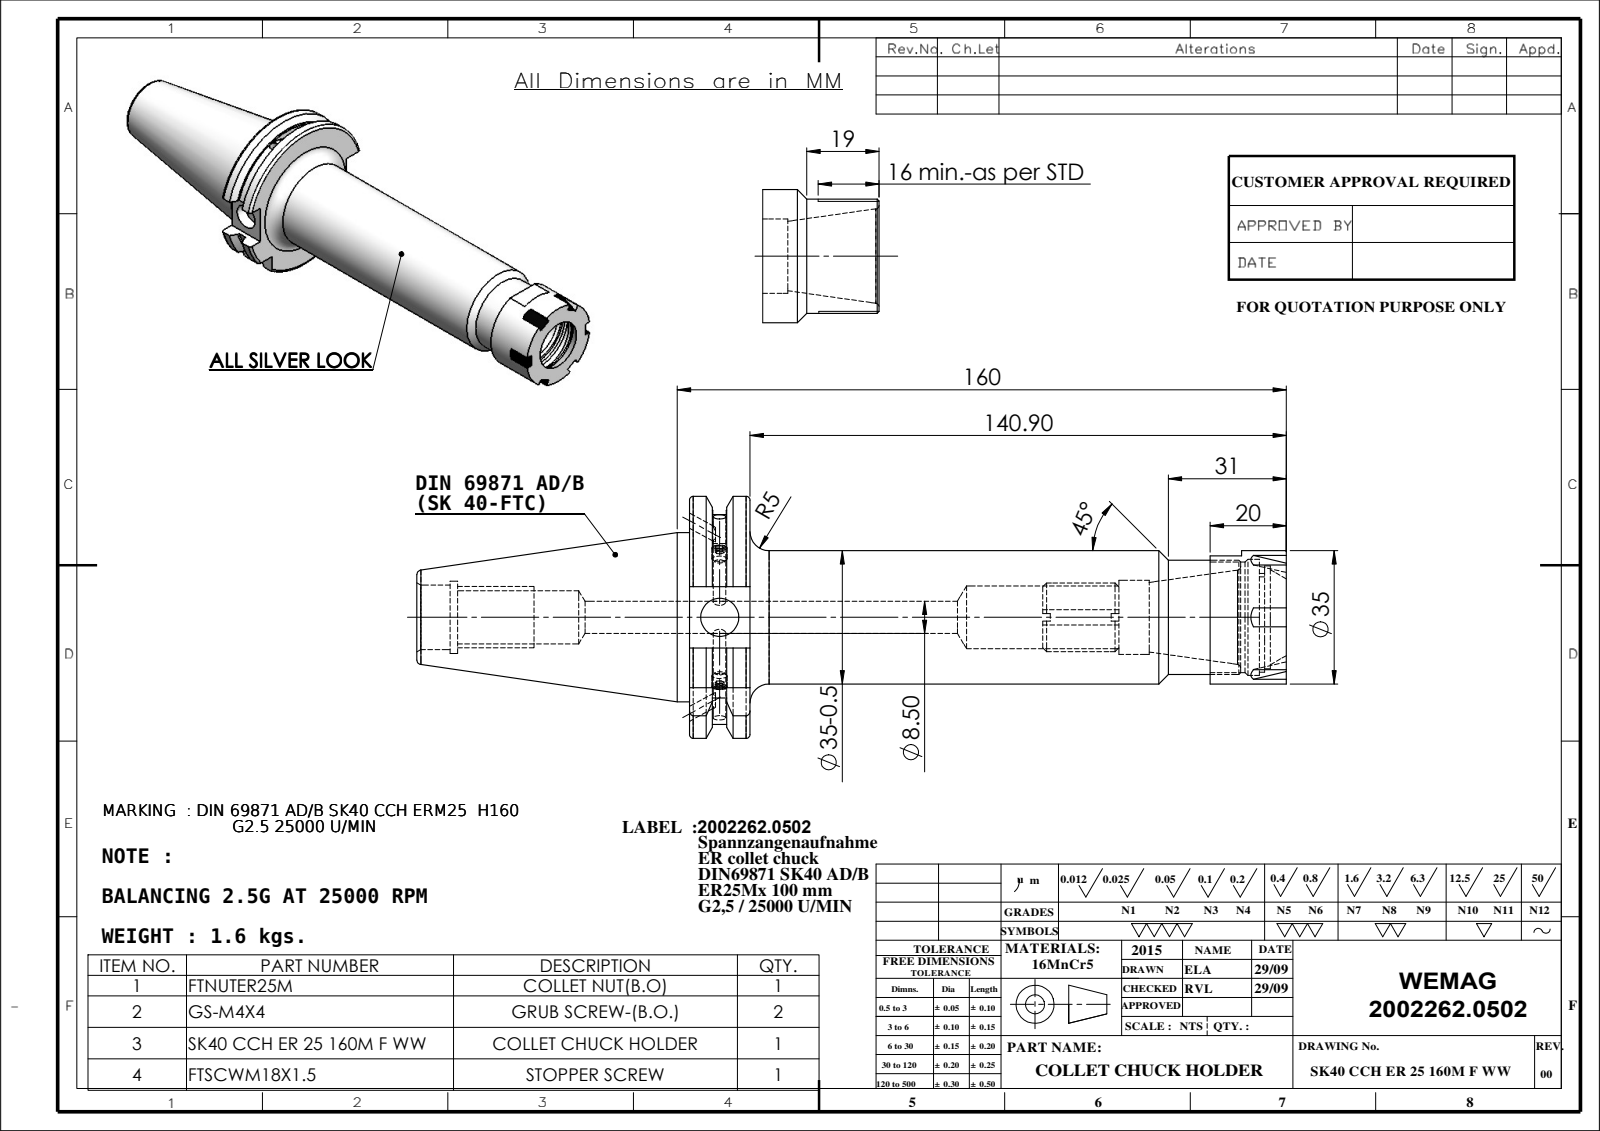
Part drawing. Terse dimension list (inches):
name: 91406-ERM725160; SK40 CCH ER 25 160M F WW; FTNUTER25M; M4X4_DIN 913 - M4 x 4-N (+1 more)
written by: SolidWorks 2009 (CONFIG_CONTROL_DESIGN)
unit: in
bodies: 5 solids, 202 faces (90 planar, 56 cylindrical, 56 other)
size: 8.992 × 2.502 × 2.42
volume: 12.83 in³; area: 72.98 in²
holes: 1× ⌀0.13, 1× ⌀0.157, 1× ⌀0.335, 1× ⌀0.394, 1× ⌀0.551, 1× ⌀0.65, 1× ⌀0.669, 1× ⌀0.748, 1× ⌀0.768, 1× ⌀1.016, 1× ⌀1.063, 1× ⌀1.142
bosses: 2× ⌀0.157, 1× ⌀1.75, 1× ⌀1.378, 1× ⌀1.181, 1× ⌀0.709
rounds: 1× R0.453, 1× R1.107, 1× R1.251
face distances: 0.626, 6.173, 5.547, 0.787, 1.732, 5.386, 4.76, 0.945, 4.441, 3.815
hole spacings: 0.059
